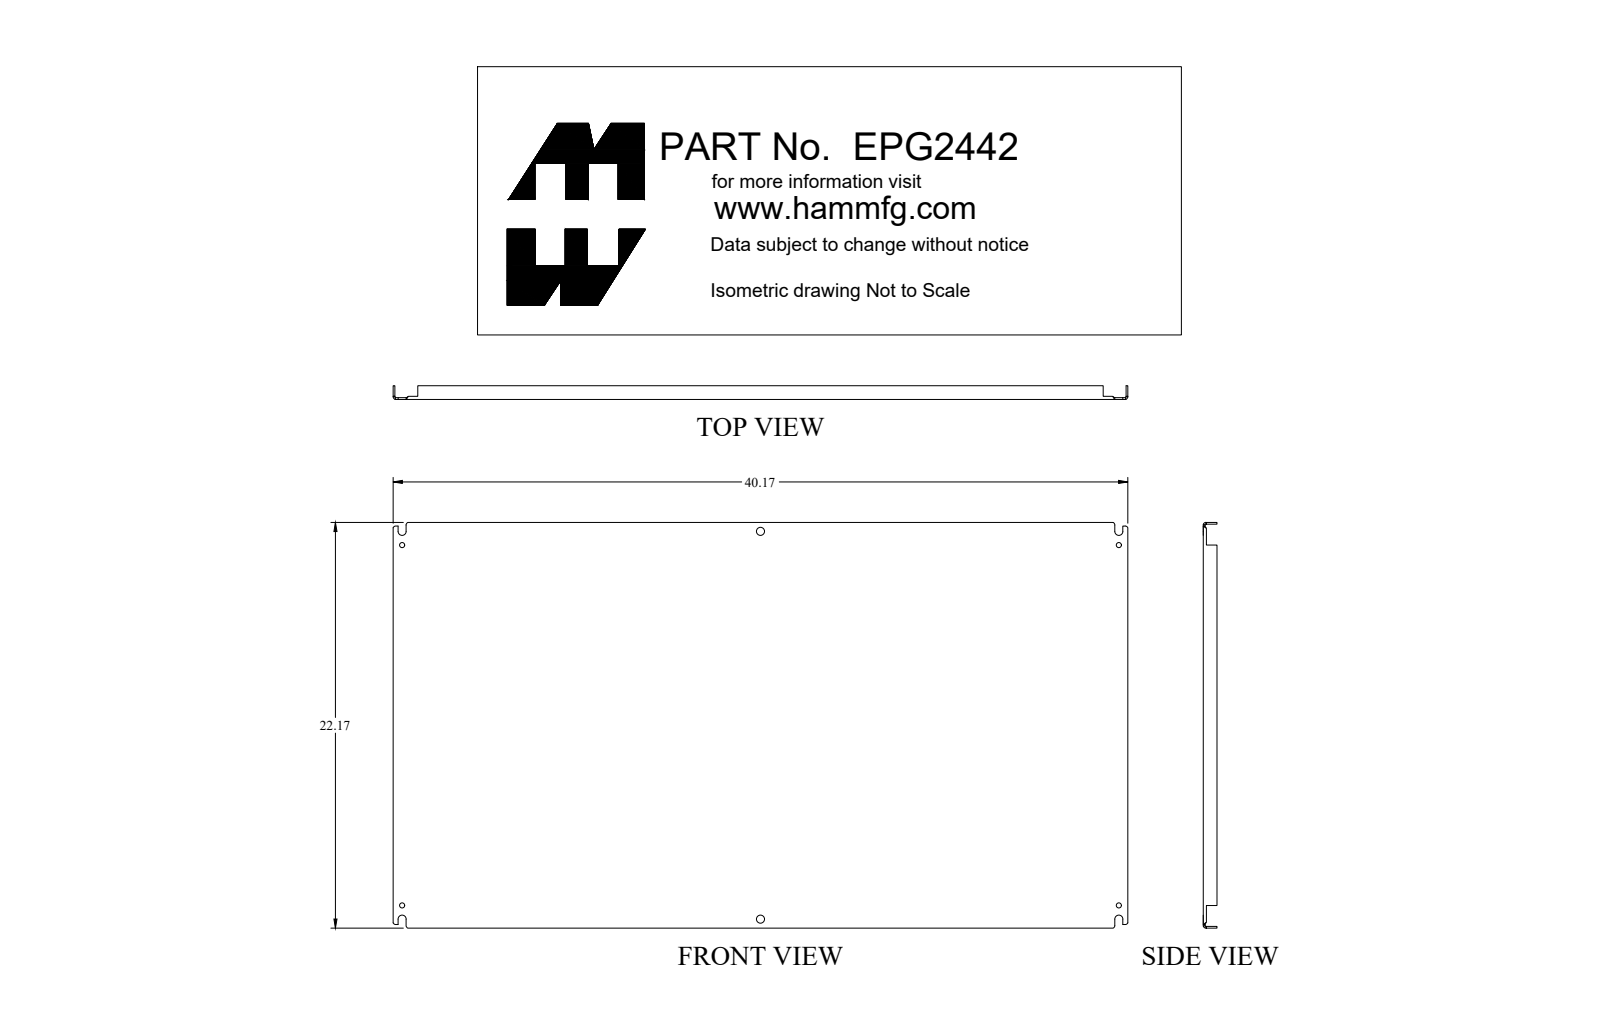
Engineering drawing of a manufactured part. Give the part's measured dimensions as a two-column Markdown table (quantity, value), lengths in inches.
| quantity | value |
| --- | --- |
| part name | EPG2442 |
| STEP written by | SolidWorks 2018 (AUTOMOTIVE_DESIGN) |
| units | inches |
| bodies | 1 solid, 132 faces (74 planar, 42 cylindrical, 16 other) |
| overall size | 40.17 × 22.17 × 0.75 |
| volume | 91.1 in³ |
| surface area | 1 931 in² |
| round holes (diameter × count) | 0.281 × 4, 0.437 × 2 |
| partial cylindrical surfaces (radius × count) | 0.048 × 4, 0.063 × 4, 0.143 × 4, 0.219 × 4 |
| main face-to-face distances | 0.095, 22.075, 40.075, 22.17, 21.98, 39.98, 40.17, 0.75, 0.655, 0.171 |
| hole center spacings | 19.608, 28.313, 19.688, 39.188, 43.856, 21.188 |
